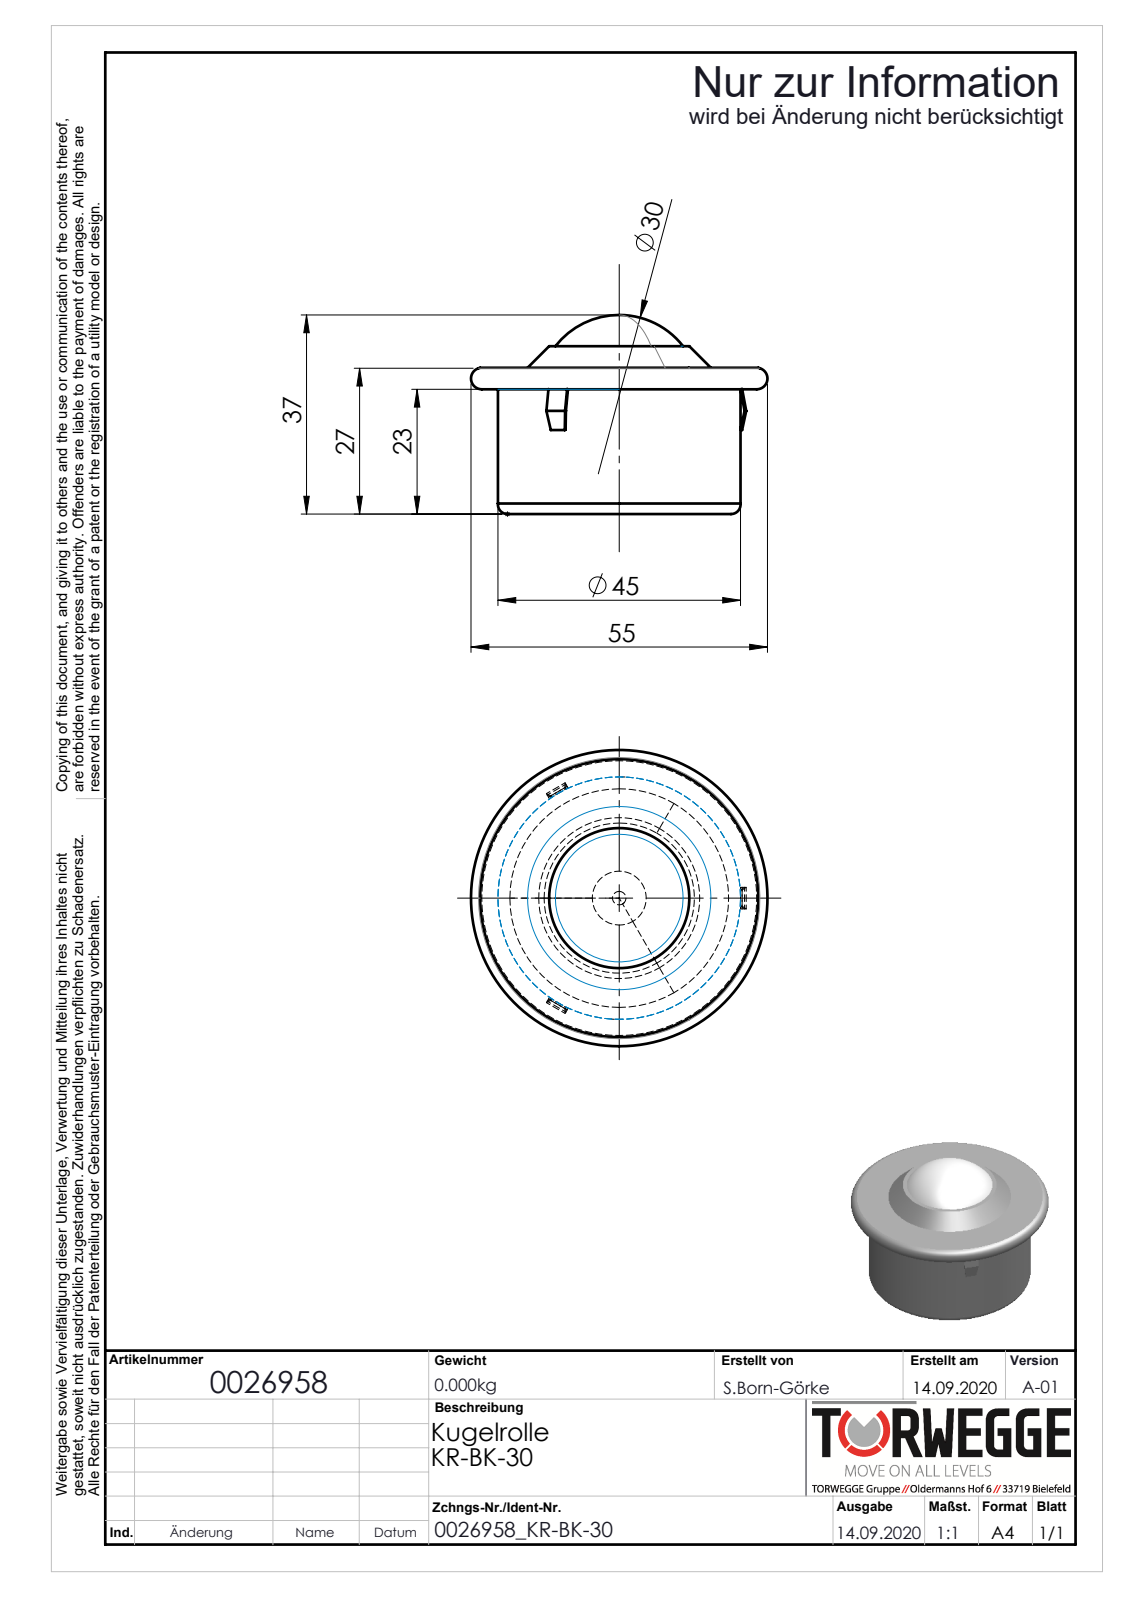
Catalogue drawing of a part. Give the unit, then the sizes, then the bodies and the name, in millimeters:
Units: millimetres
Overall size (bounding box): 55 × 55 × 36.96
Round holes (diameter × count): ⌀2.5 ×1, ⌀10 ×1
Round bosses / shafts (diameter × count): ⌀45 ×1
Main face-to-face distances: 4, 8
Bodies: 0 solids, 73 faces (34 planar, 6 cylindrical, 33 other)
Part name (STEP PRODUCT): 0026958
STEP written by: SolidWorks 2018 (AUTOMOTIVE_DESIGN)
